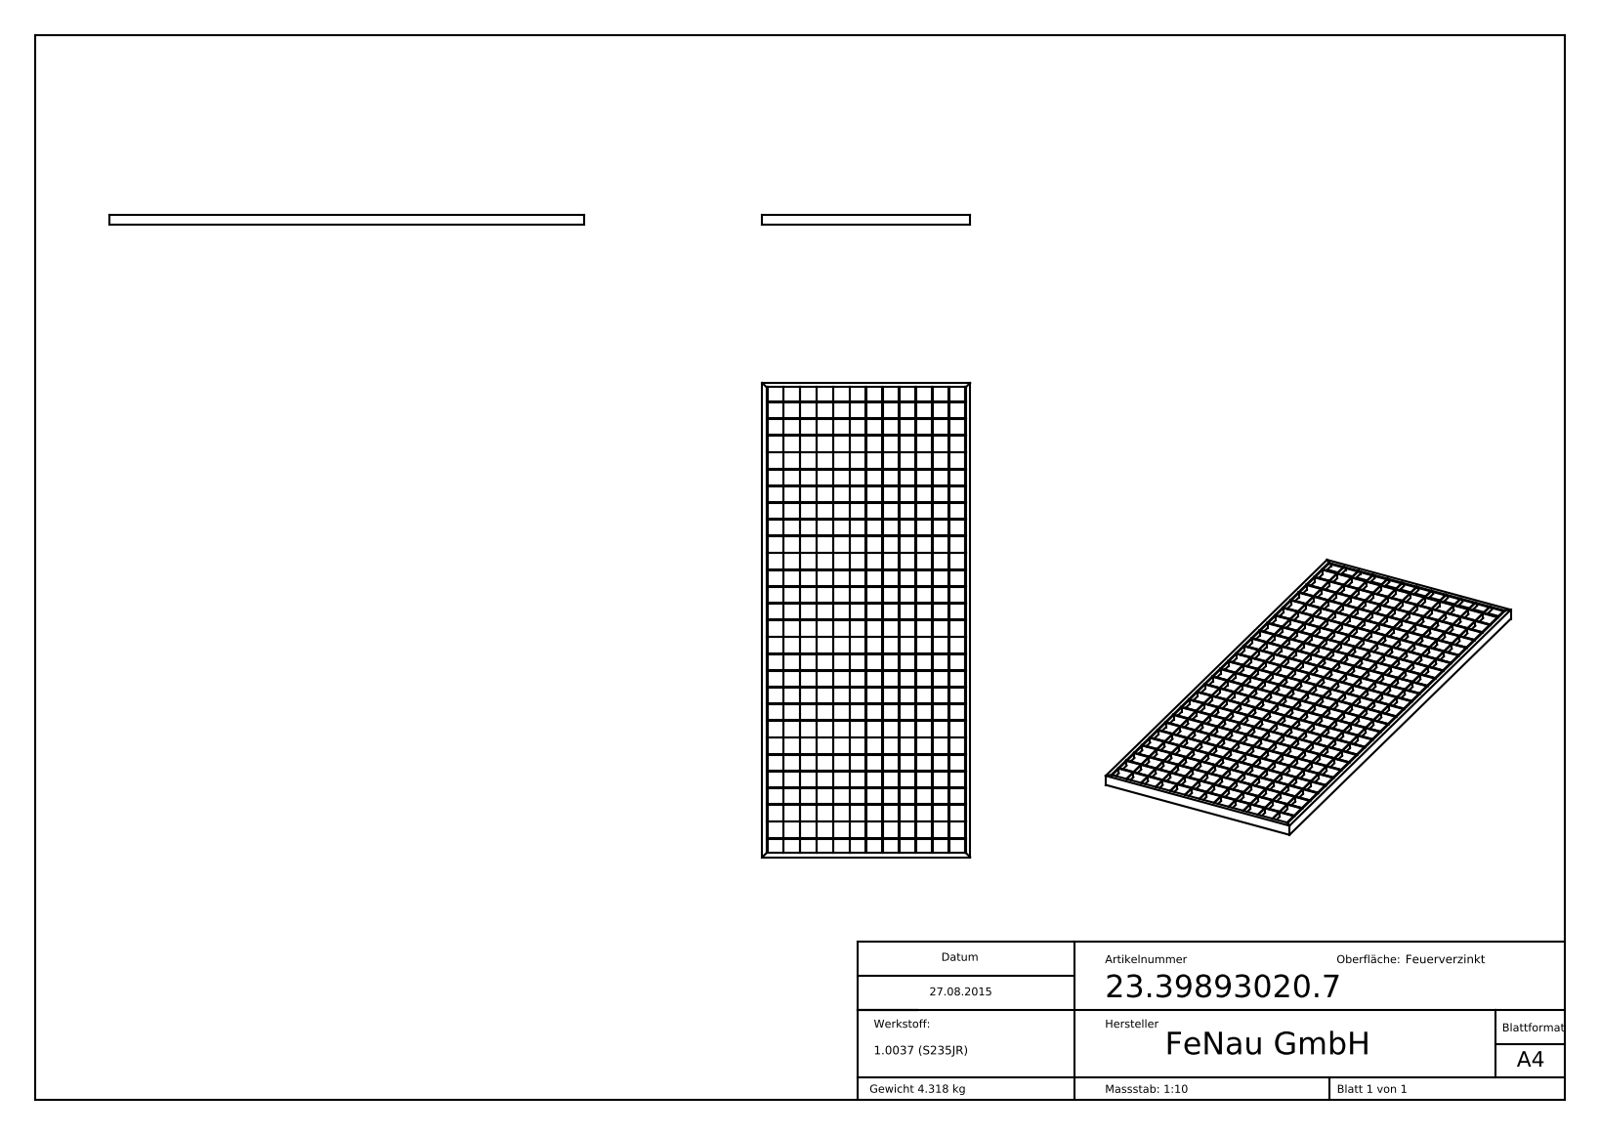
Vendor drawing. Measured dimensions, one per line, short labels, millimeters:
name: 23-39893020-7
written by: SolidWorks 2015 (CONFIG_CONTROL_DESIGN)
unit: mm
bodies: 1 solid, 1380 faces (1380 planar, 0 cylindrical, 0 other)
size: 890 × 390 × 20
volume: 553 611 mm³; area: 820 287 mm²
face distances: 63, 31.5, 94.5, 31, 126, 157.5, 189, 62, 220.5, 252
